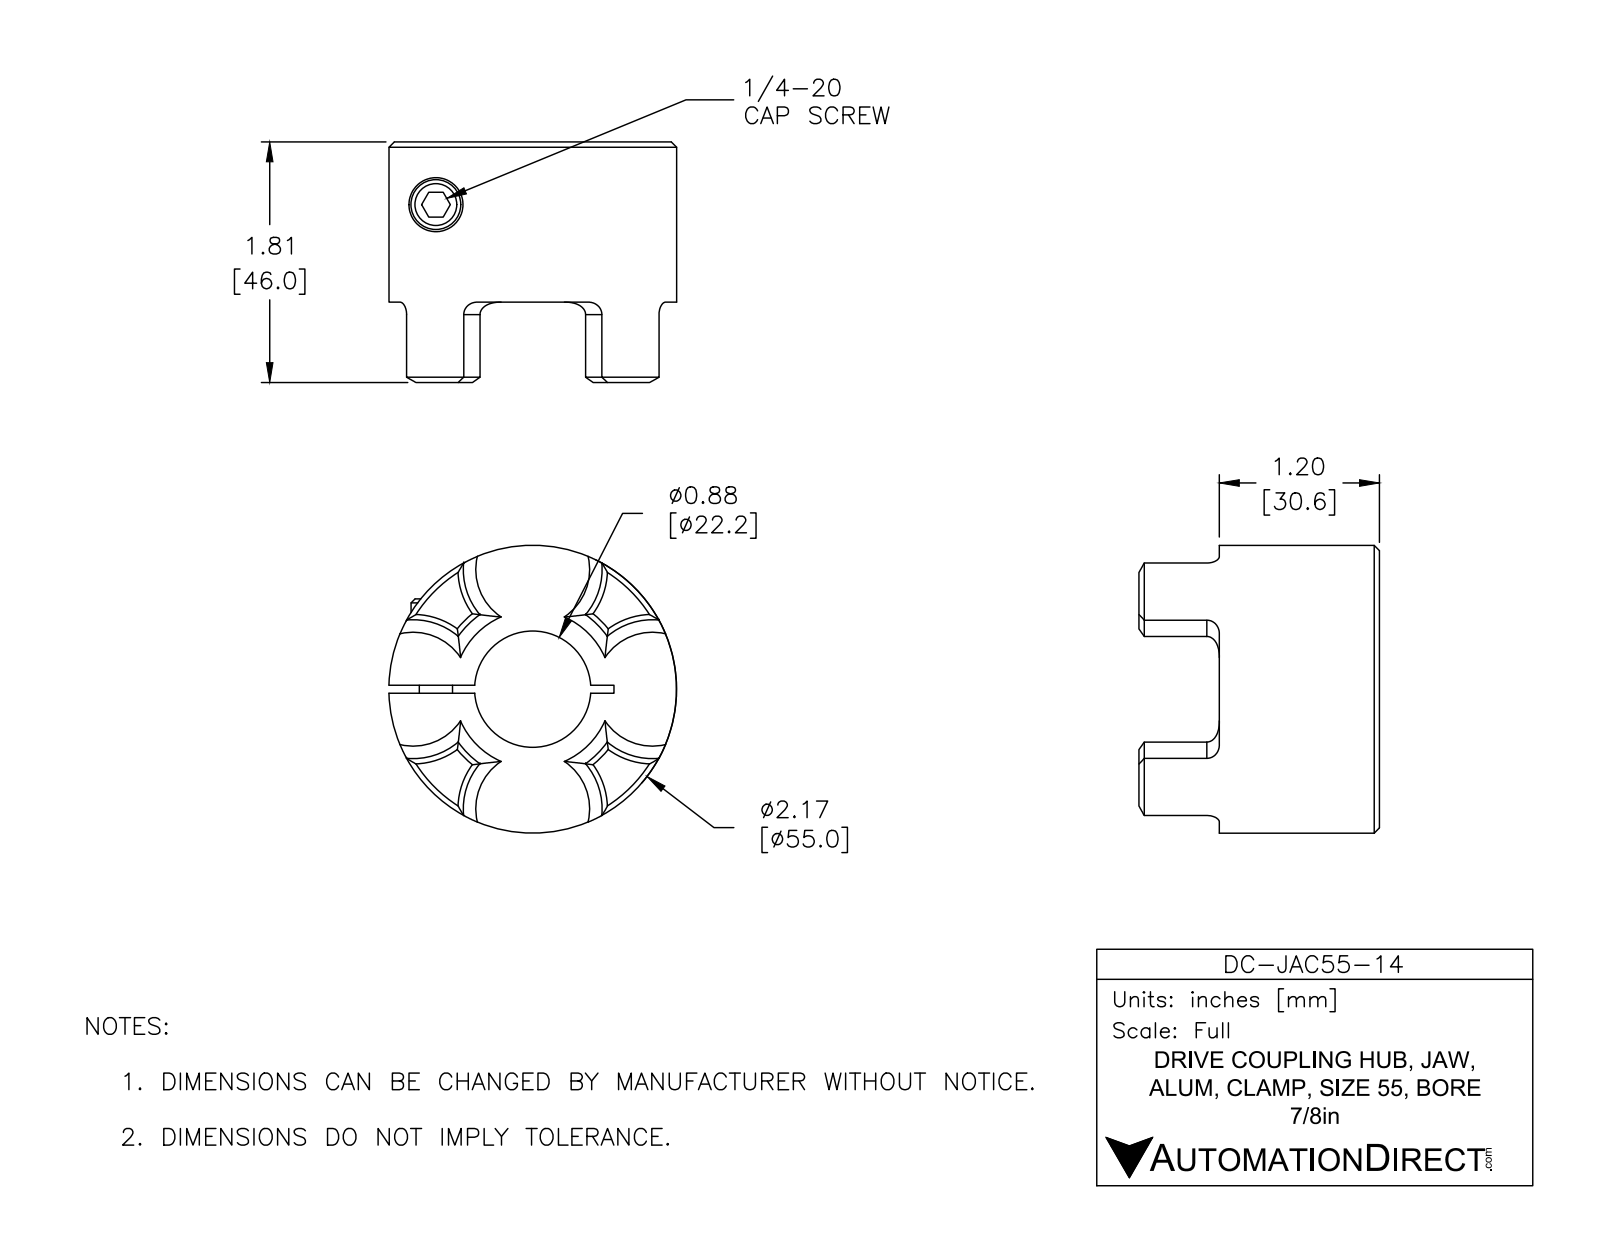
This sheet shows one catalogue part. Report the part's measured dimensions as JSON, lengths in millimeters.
{"part_name": "DC-JA55-14_POST2016", "step_written_by": "SolidWorks 2016 (AUTOMOTIVE_DESIGN)", "units": "millimeters", "bodies": {"solids": 2, "faces": 92, "planar": 22, "cylindrical": 29, "other": 41}, "overall_size": [55.6, 55, 46], "volume_mm3": 64680, "surface_area_mm2": 16300, "round_holes": [[6.8, 1], [10.3, 1], [22.2, 1]], "round_bosses_or_shafts": [[55, 1], [9.5, 1], [6.4, 1]], "partial_cylinders_radius": [[13.3, 4], [17.4, 1]], "face_to_face_distances": [30.6, 1.5, 46, 15.4, 11.7, 10.2, 4.7, 7.4, 8.9, 19.1]}
